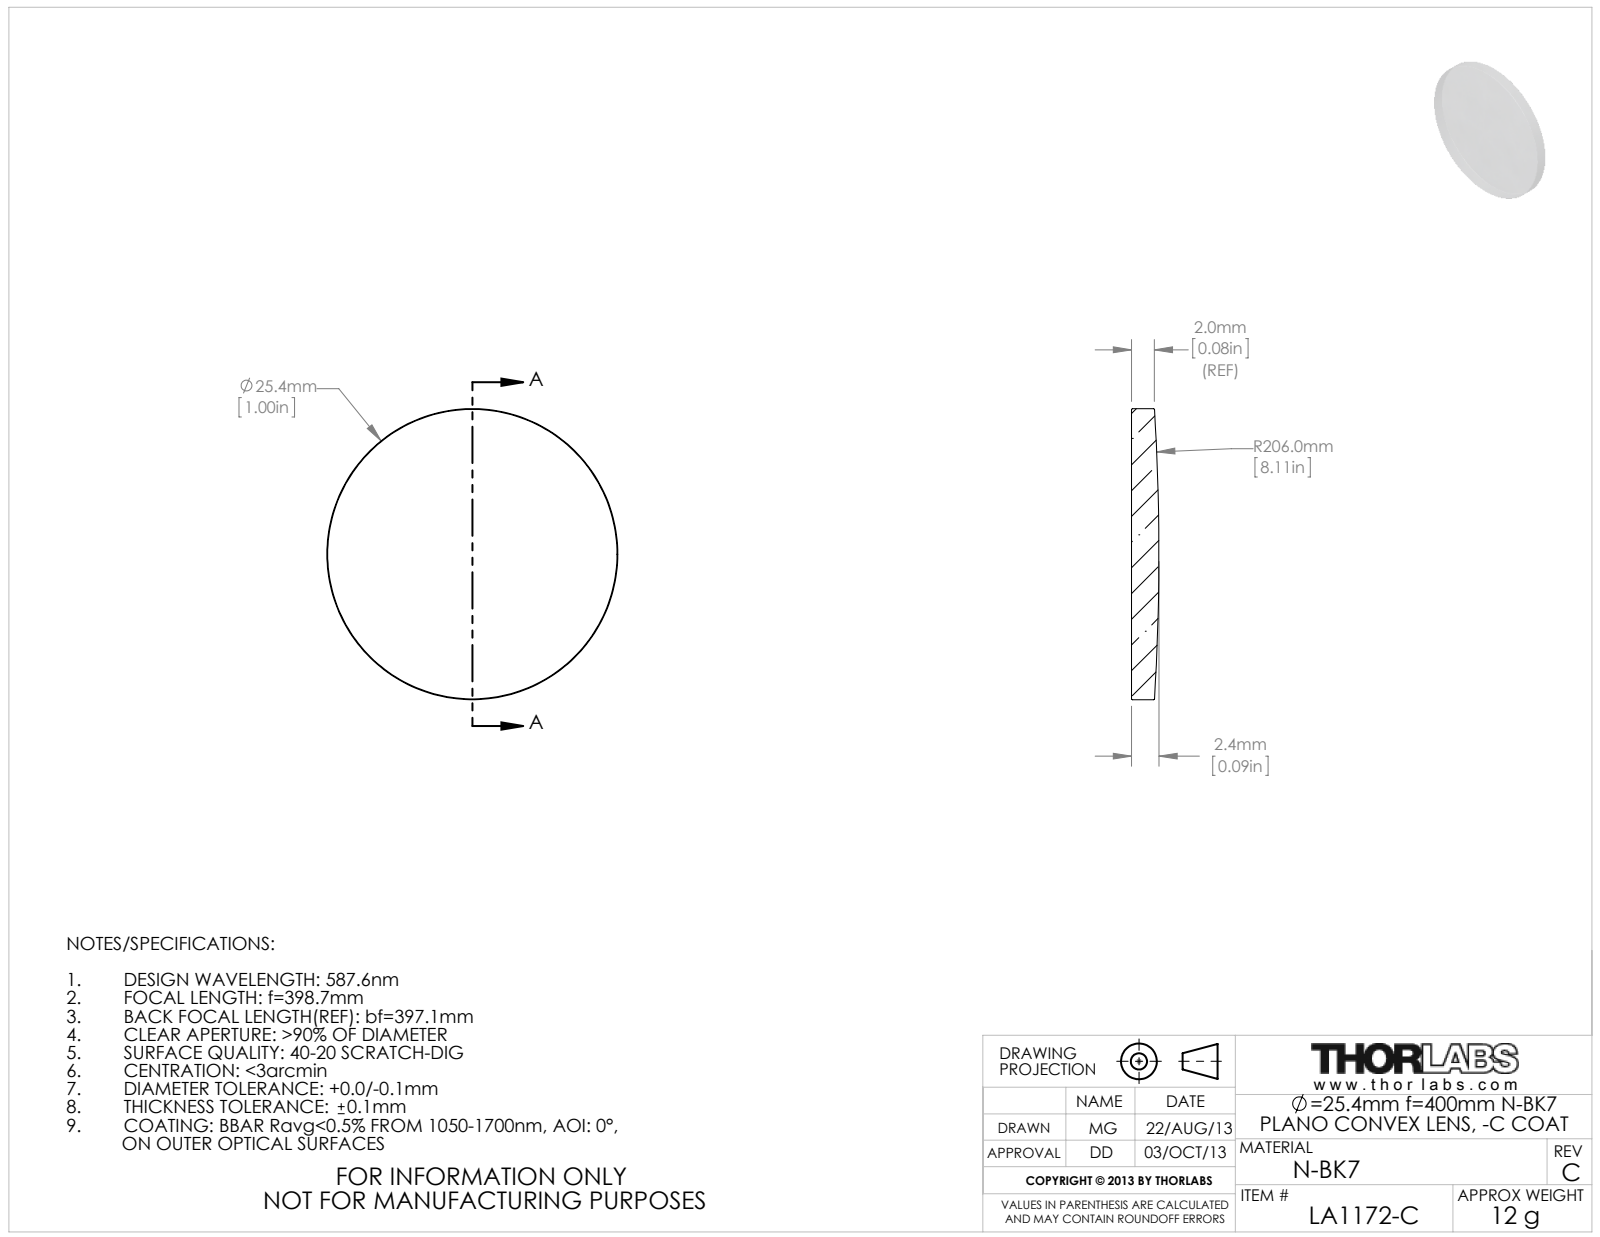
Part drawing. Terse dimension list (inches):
name: 4591-E0W
written by: SolidWorks 2009 (AUTOMOTIVE_DESIGN)
unit: in
bodies: 1 solid, 5 faces (1 planar, 2 cylindrical, 2 other)
size: 1 × 1 × 0.094
volume: 0.068 in³; area: 1.818 in²
bosses: 1× ⌀1
